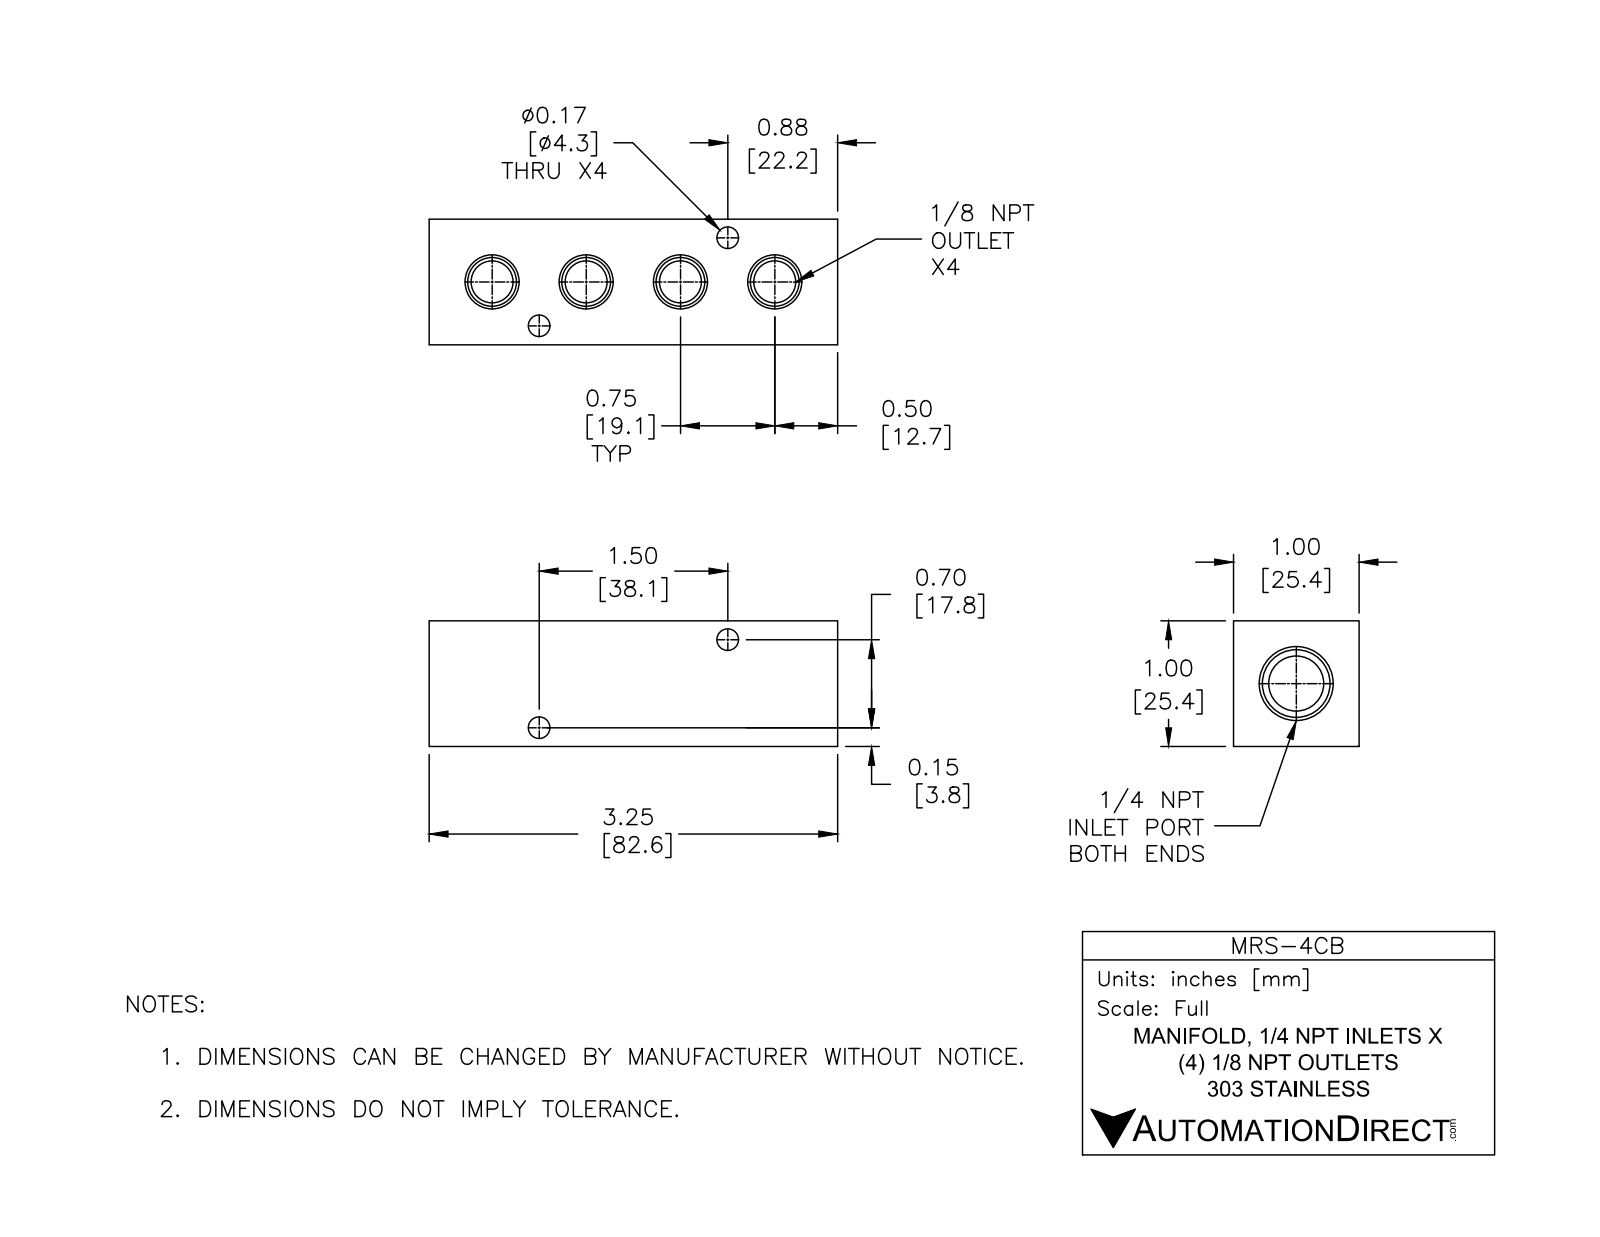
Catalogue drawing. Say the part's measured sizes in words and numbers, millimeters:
The part is named "MRS-4CB". Its 3-D file was written by "SolidWorks 2015 (CONFIG_CONTROL_DESIGN)". It is 1 solid with 61 faces: 12 planar, 25 cylindrical and 24 other. Overall it measures 82.6 by 25.4 by 25.4 millimeters. Its volume is 40 610 cubic millimeters and its surface area 14 000 square millimeters. Round holes: 4 of diameter 4.3, 2 of diameter 8.4, 1 of diameter 11.1. Partial cylindrical surfaces (rounded edges, fillets, slot ends): 2 of radius 4.2. The main face-to-face distances are 25.4, 82.6, 18.5, 6.9, 9.9, 72.6, 62.7. The hole center spacings are 13, 42, 19.1, 29.9, 29.9.
